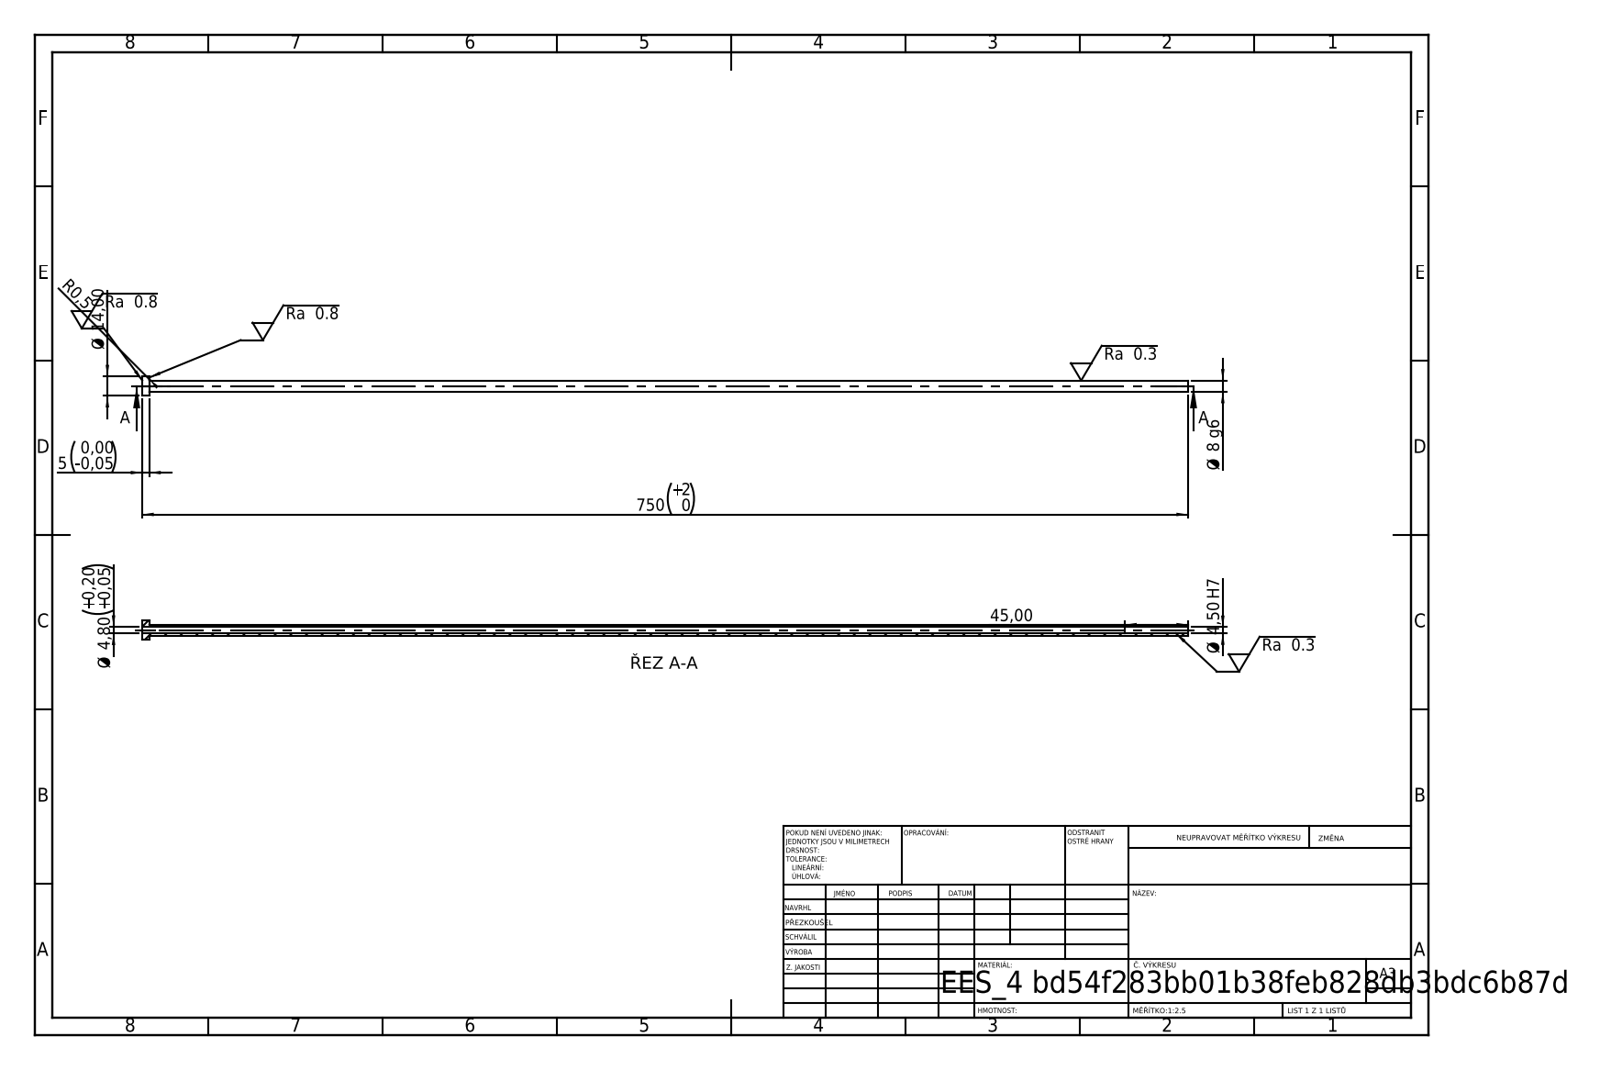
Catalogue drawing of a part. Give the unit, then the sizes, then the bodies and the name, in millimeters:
Units: millimetres
Overall size (bounding box): 750 × 14 × 14
Round holes (diameter × count): ⌀4.5 ×1, ⌀4.8 ×1
Round bosses / shafts (diameter × count): ⌀14 ×1, ⌀8 ×1
Main face-to-face distances: 5, 750, 745, 705, 700, 45
Volume: 24 746 mm³ · Surface area: 30 482 mm²
Bodies: 1 solid, 14 faces (4 planar, 8 cylindrical, 2 other)
STEP written by: SolidWorks 2019 (CONFIG_CONTROL_DESIGN)
